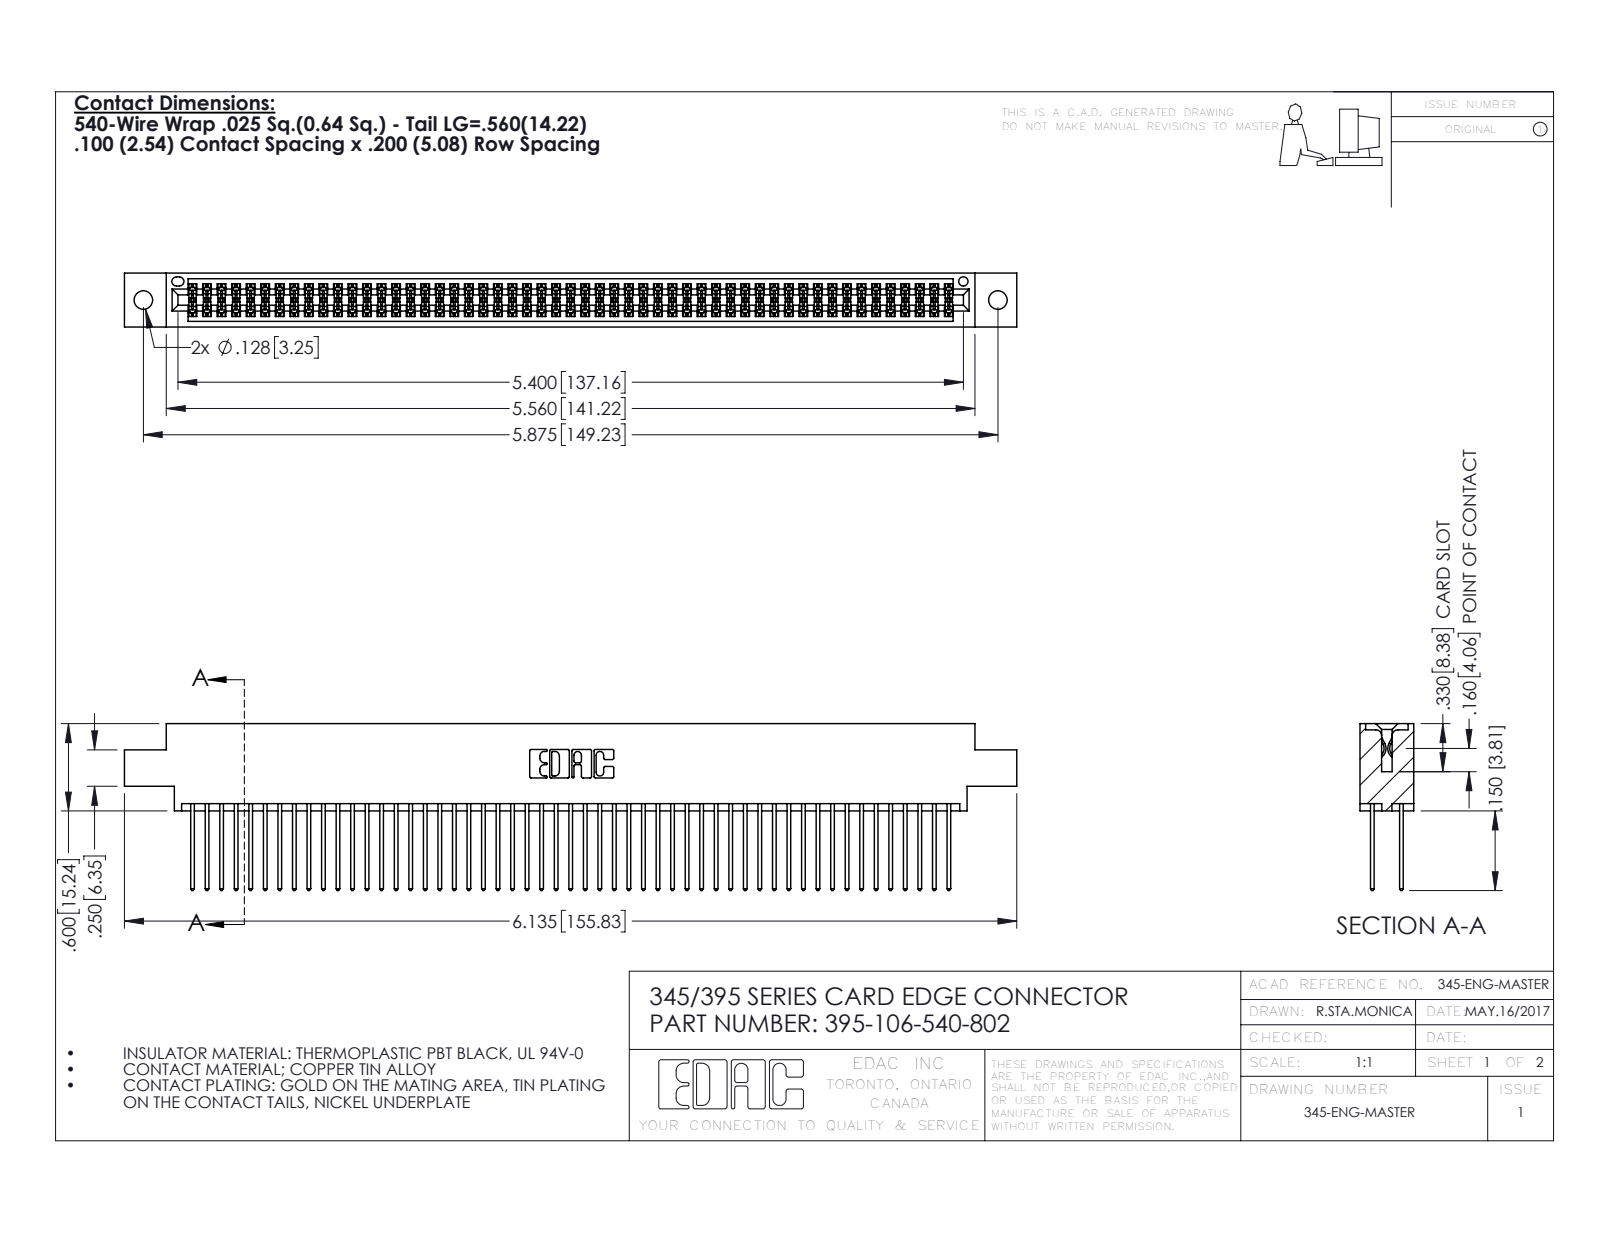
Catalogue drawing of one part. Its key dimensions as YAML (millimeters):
part_name: "345-292-001_345-293-140; 345 Part_0.170 Offset - 0.128 Dia; 395-106-540-802"
step_written_by: "SolidWorks 2016 (CONFIG_CONTROL_DESIGN)"
units: millimeters
bodies: {solids: 107, faces: 5430, planar: 3582, cylindrical: 1848, other: 0}
overall_size: [155.8, 29.1, 9.4]
volume: 15500
surface_area: 24850
round_holes:
  - {diameter: 3.3, count: 2}
  - {diameter: 1.6, count: 1}
partial_cylinders:
  - {radius: 0.2, count: 159}
  - {radius: 0.3, count: 106}
  - {radius: 0.3, count: 22}
  - {radius: 0.2, count: 6}
  - {radius: 0.8, count: 6}
  - {radius: 0.7, count: 3}
  - {radius: 0.4, count: 2}
  - {radius: 0.5, count: 2}
face_to_face_distances: [1.8, 7.6, 5.1, 2.5, 6.9, 0.6, 9.4, 5.7, 4.4, 3.8]
hole_center_spacings: [6.9, 143.2, 149.2]
